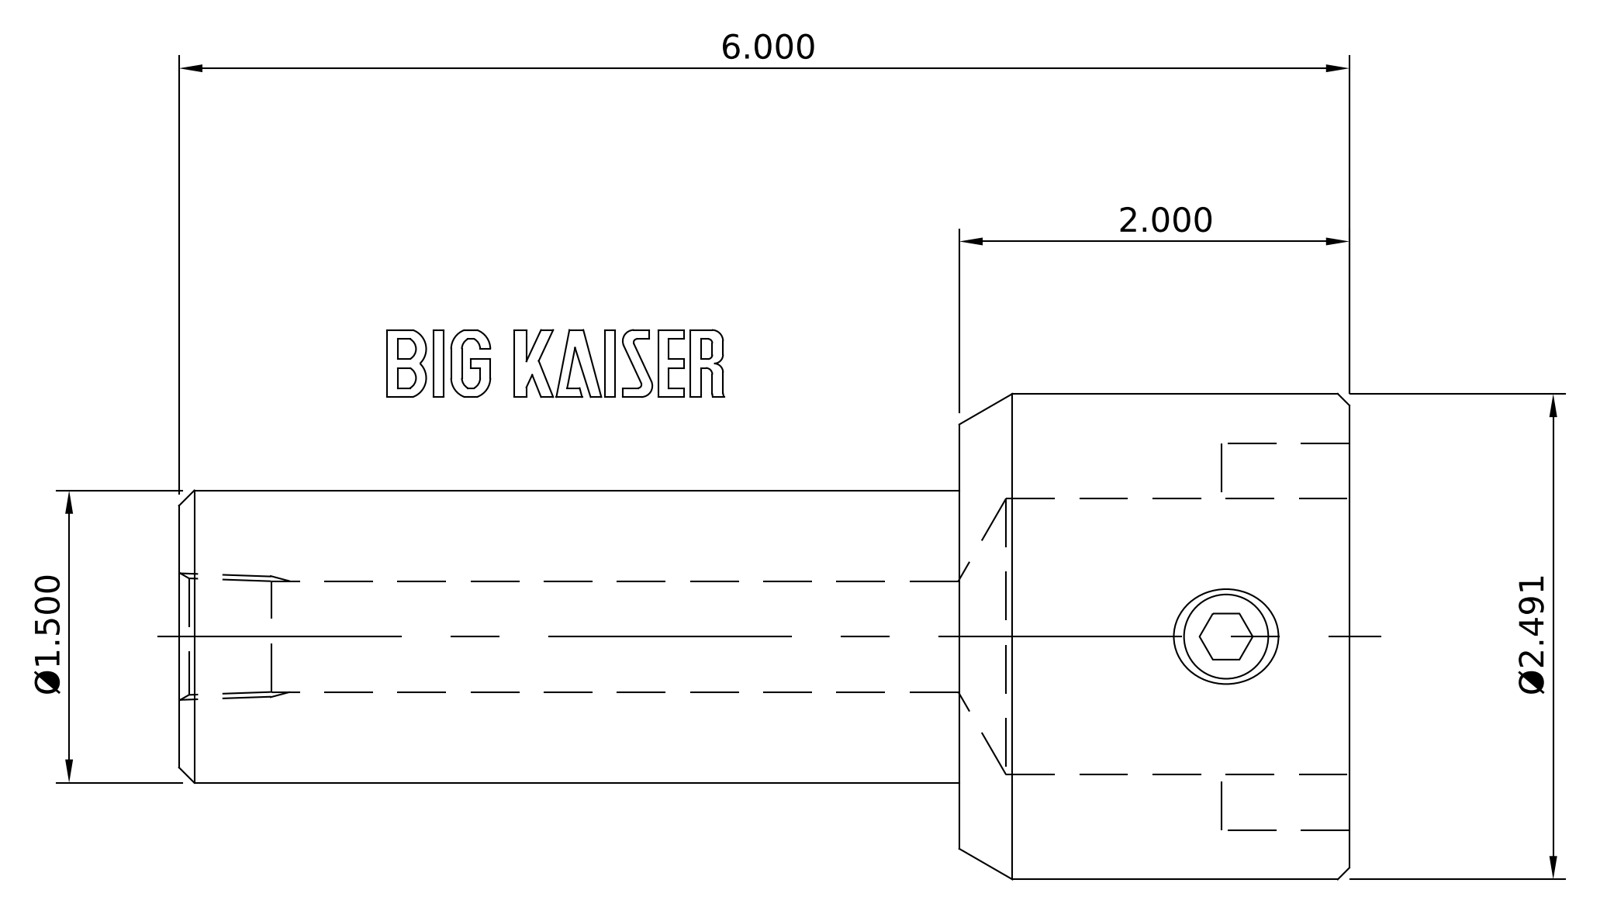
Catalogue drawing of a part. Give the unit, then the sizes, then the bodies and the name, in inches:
Units: inches
Overall size (bounding box): 6 × 2.491 × 2.491
Round holes (diameter × count): ⌀0.402 ×1, ⌀0.468 ×1, ⌀0.484 ×1, ⌀0.567 ×1, ⌀1.299 ×1, ⌀1.417 ×1, ⌀1.437 ×1
Round bosses / shafts (diameter × count): ⌀2.491 ×1, ⌀1.5 ×1
Partial cylindrical surfaces — rounded edges, fillets, slot ends (radius × count): R0.217 ×2
Main face-to-face distances: 2, 4, 6, 0.522, 1.209, 4.346, 0.346, 1.654, 5.346, 1.346
Hole centre spacings: 0.986
Volume: 11.97 in³ · Surface area: 58.37 in²
Bodies: 1 solid, 43 faces (21 planar, 11 cylindrical, 11 other)
Part name (STEP PRODUCT): 11.361.262
STEP written by: SolidWorks 2018 (CONFIG_CONTROL_DESIGN)
